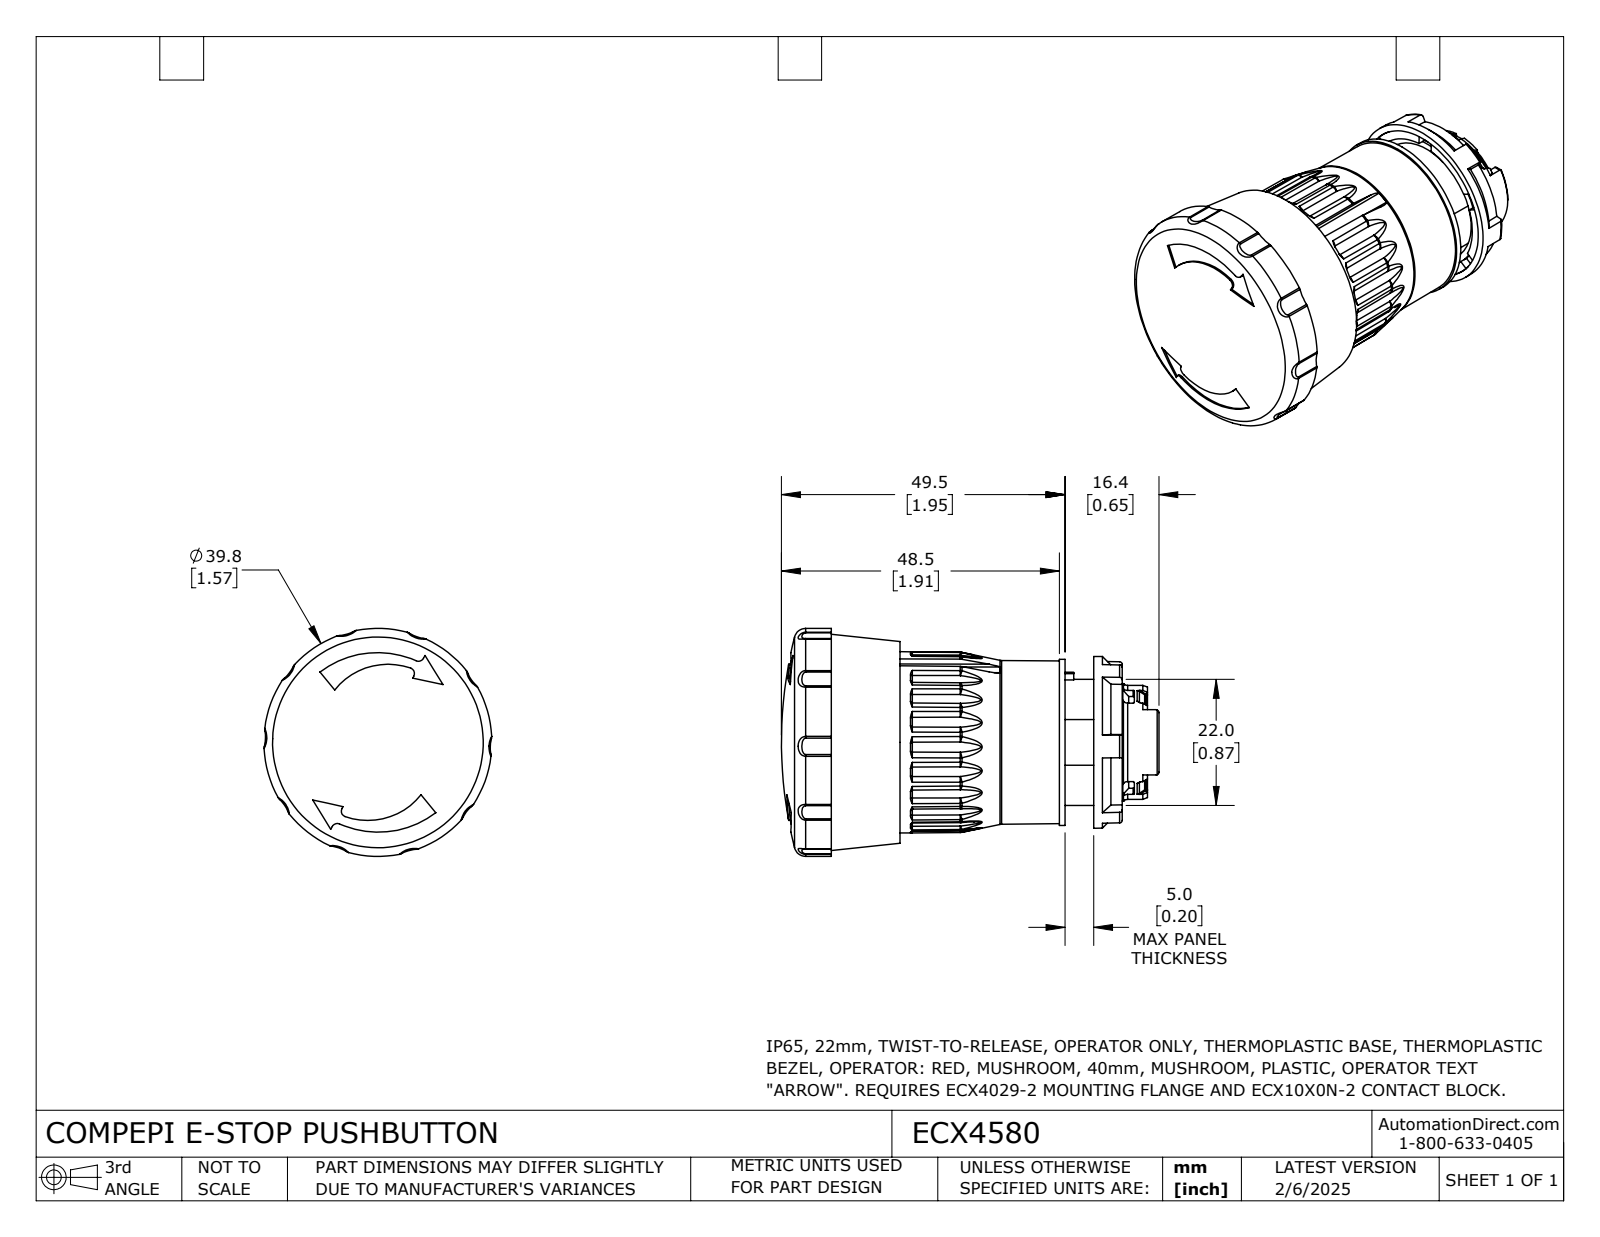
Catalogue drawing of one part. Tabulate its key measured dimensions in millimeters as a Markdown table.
| quantity | value |
| --- | --- |
| part name | ECX4580 |
| STEP written by | SolidWorks 2024 (CONFIG_CONTROL_DESIGN) |
| units | millimeters |
| bodies | 4 solids, 889 faces (220 planar, 164 cylindrical, 505 other) |
| overall size | 65.9 × 39.8 × 39.8 |
| volume | 28 710 mm³ |
| surface area | 24 050 mm² |
| round holes (diameter × count) | 0.6 × 1, 1.3 × 1, 18.1 × 1, 21.7 × 1, 22.1 × 1 |
| round bosses / shafts (diameter × count) | 29 × 1, 24.5 × 1, 23.5 × 1, 22.2 × 1, 21.4 × 1, 20.5 × 1, 20 × 1 |
| partial cylindrical surfaces (radius × count) | 1 × 28, 0.2 × 24, 0.5 × 14, 6.8 × 10, 0.3 × 2, 0.4 × 2, 0.7 × 2, 11.9 × 2 |
| main face-to-face distances | 45.8, 1, 46.8, 6, 4.9, 11, 18, 9.9, 10.9, 56.7 |
| hole center spacings | 8.3, 11.1, 14.4 |
